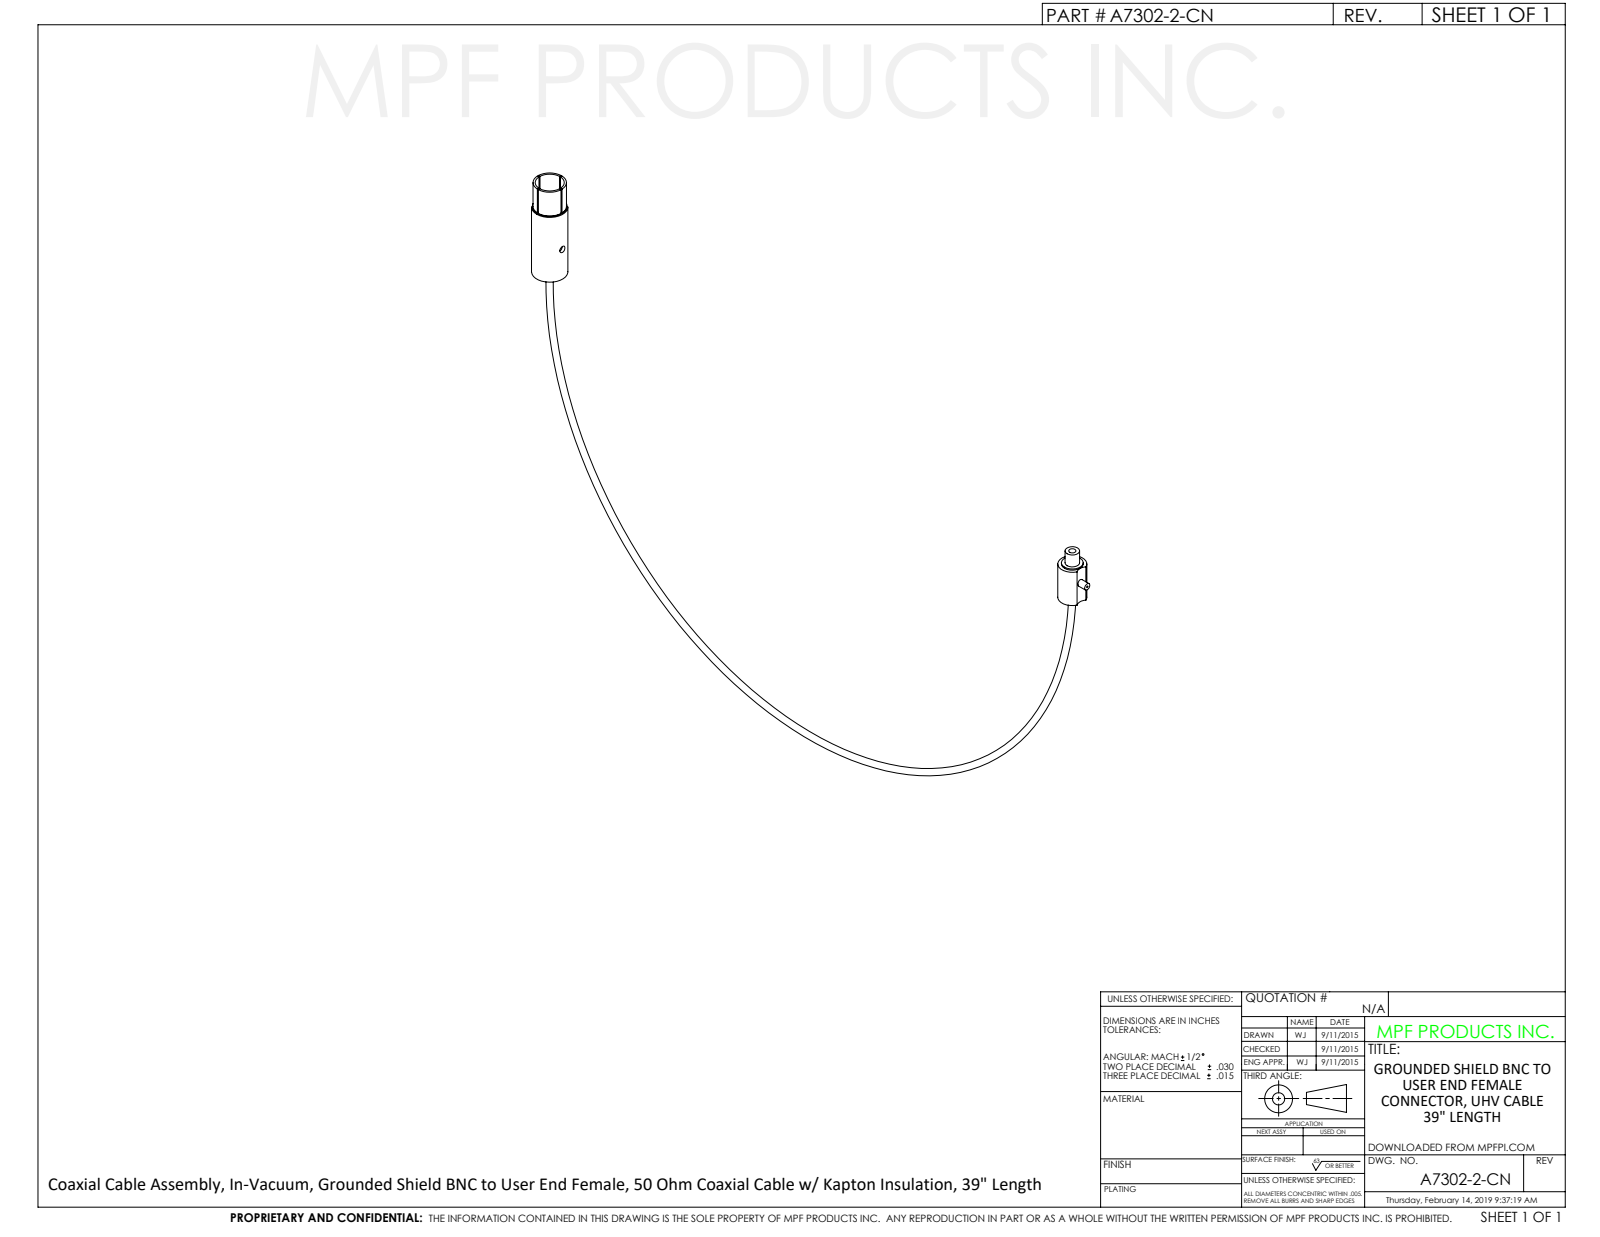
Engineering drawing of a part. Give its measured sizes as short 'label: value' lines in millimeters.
name: A7302-2-CN
written by: SolidWorks 2012 (CONFIG_CONTROL_DESIGN)
unit: mm
bodies: 1 solid, 58 faces (25 planar, 28 cylindrical, 5 other)
size: 279.2 × 173.6 × 20.3
volume: 15 100 mm³; area: 9 794 mm²
holes: 3× ⌀2.5, 1× ⌀0.6, 1× ⌀12.7
bosses: 1× ⌀20.3, 1× ⌀19.1, 1× ⌀18, 1× ⌀15.2, 1× ⌀10.2, 1× ⌀2.8, 1× ⌀2.6
rounds: 1× R3.5
face distances: 10.1, 18.1, 8, 48.2, 38.1, 30.1, 15.2, 5.1, 2.9, 33
hole spacings: 14.7, 258.1
